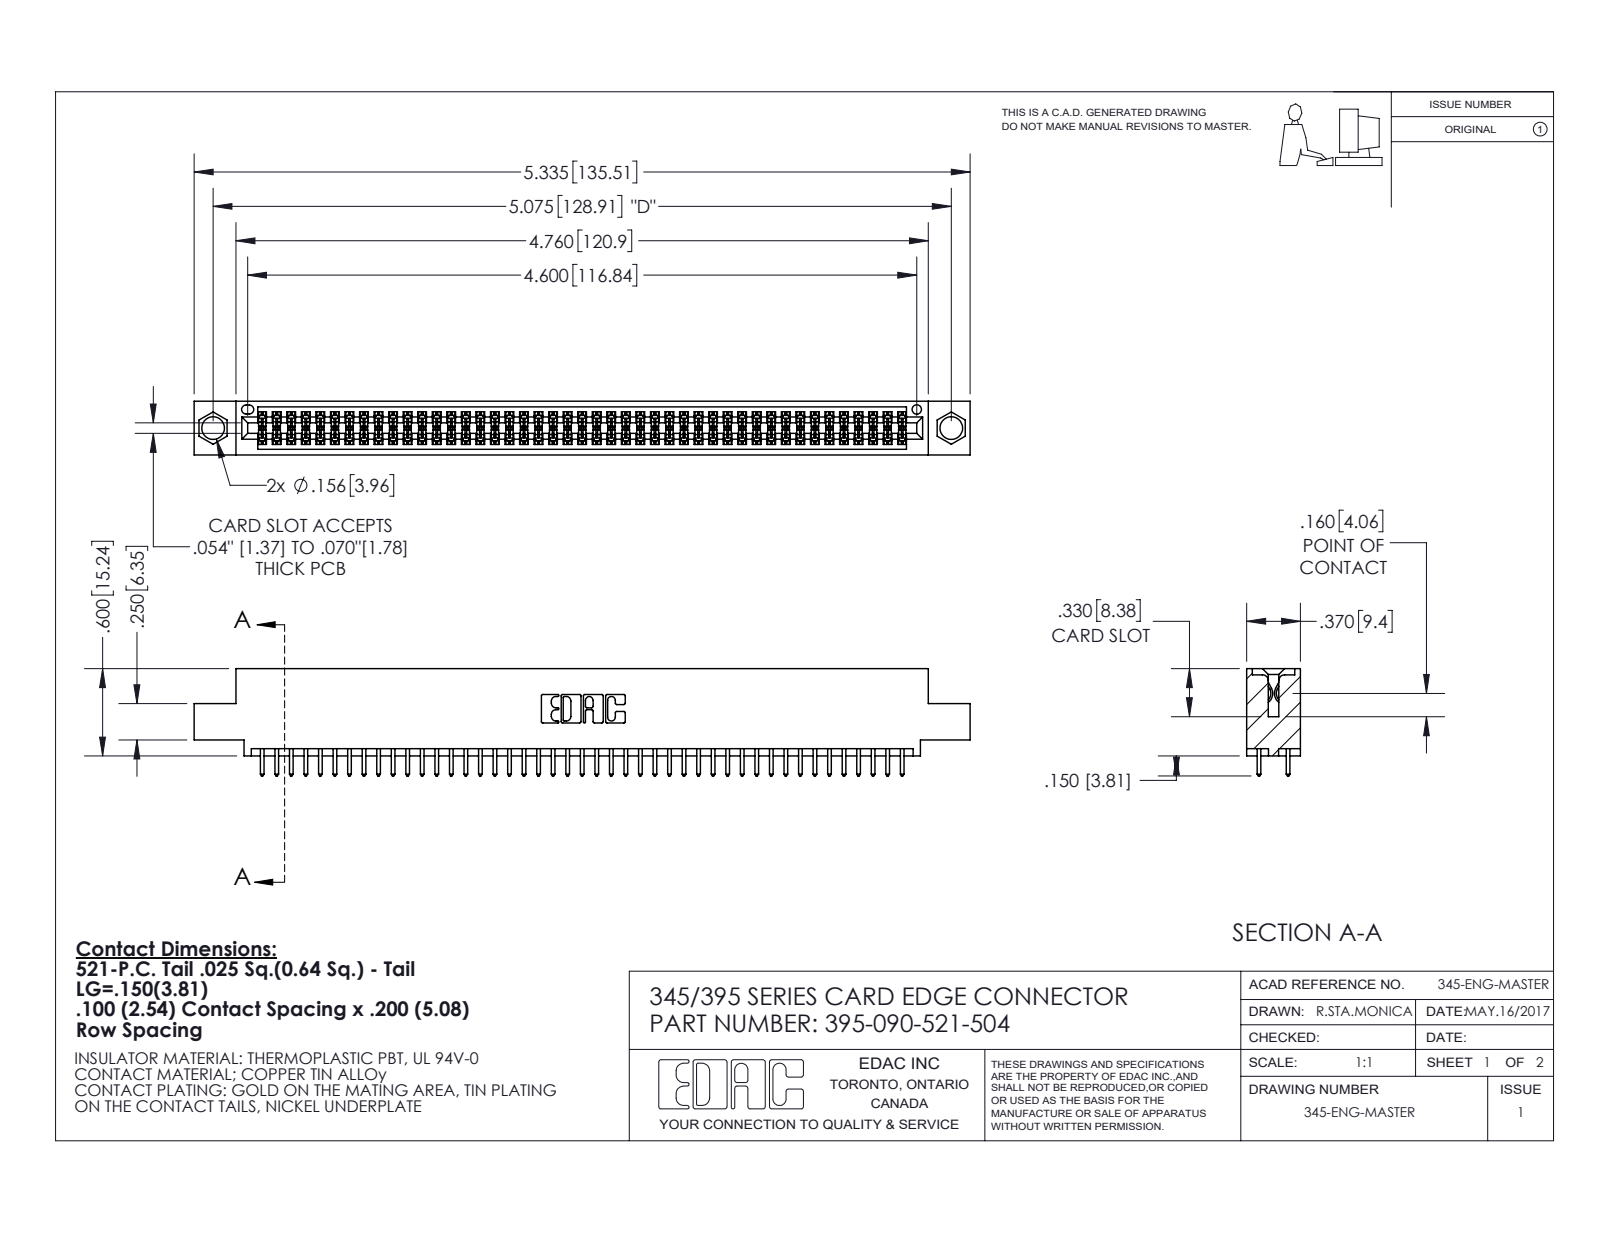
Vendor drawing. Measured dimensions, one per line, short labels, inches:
name: 395-090-521-504; 345 Part_0.110 Offset - 0.156 Dia-TI; 345-292-001_345-293-121
written by: SolidWorks 2020 (CONFIG_CONTROL_DESIGN)
unit: in
bodies: 91 solids, 4644 faces (3068 planar, 1576 cylindrical, 0 other)
size: 5.335 × 0.737 × 0.37
volume: 0.792 in³; area: 29.36 in²
holes: 2× ⌀0.156, 1× ⌀0.064
rounds: 180× R0.006, 90× R0.01, 22× R0.01, 6× R0.007, 6× R0.031, 3× R0.026, 2× R0.014, 2× R0.019
face distances: 0.072, 0.298, 0.2, 0.37, 0.098, 0.272, 0.025, 0.225, 0.175, 0.149
hole spacings: 0.27, 4.839, 5.075
